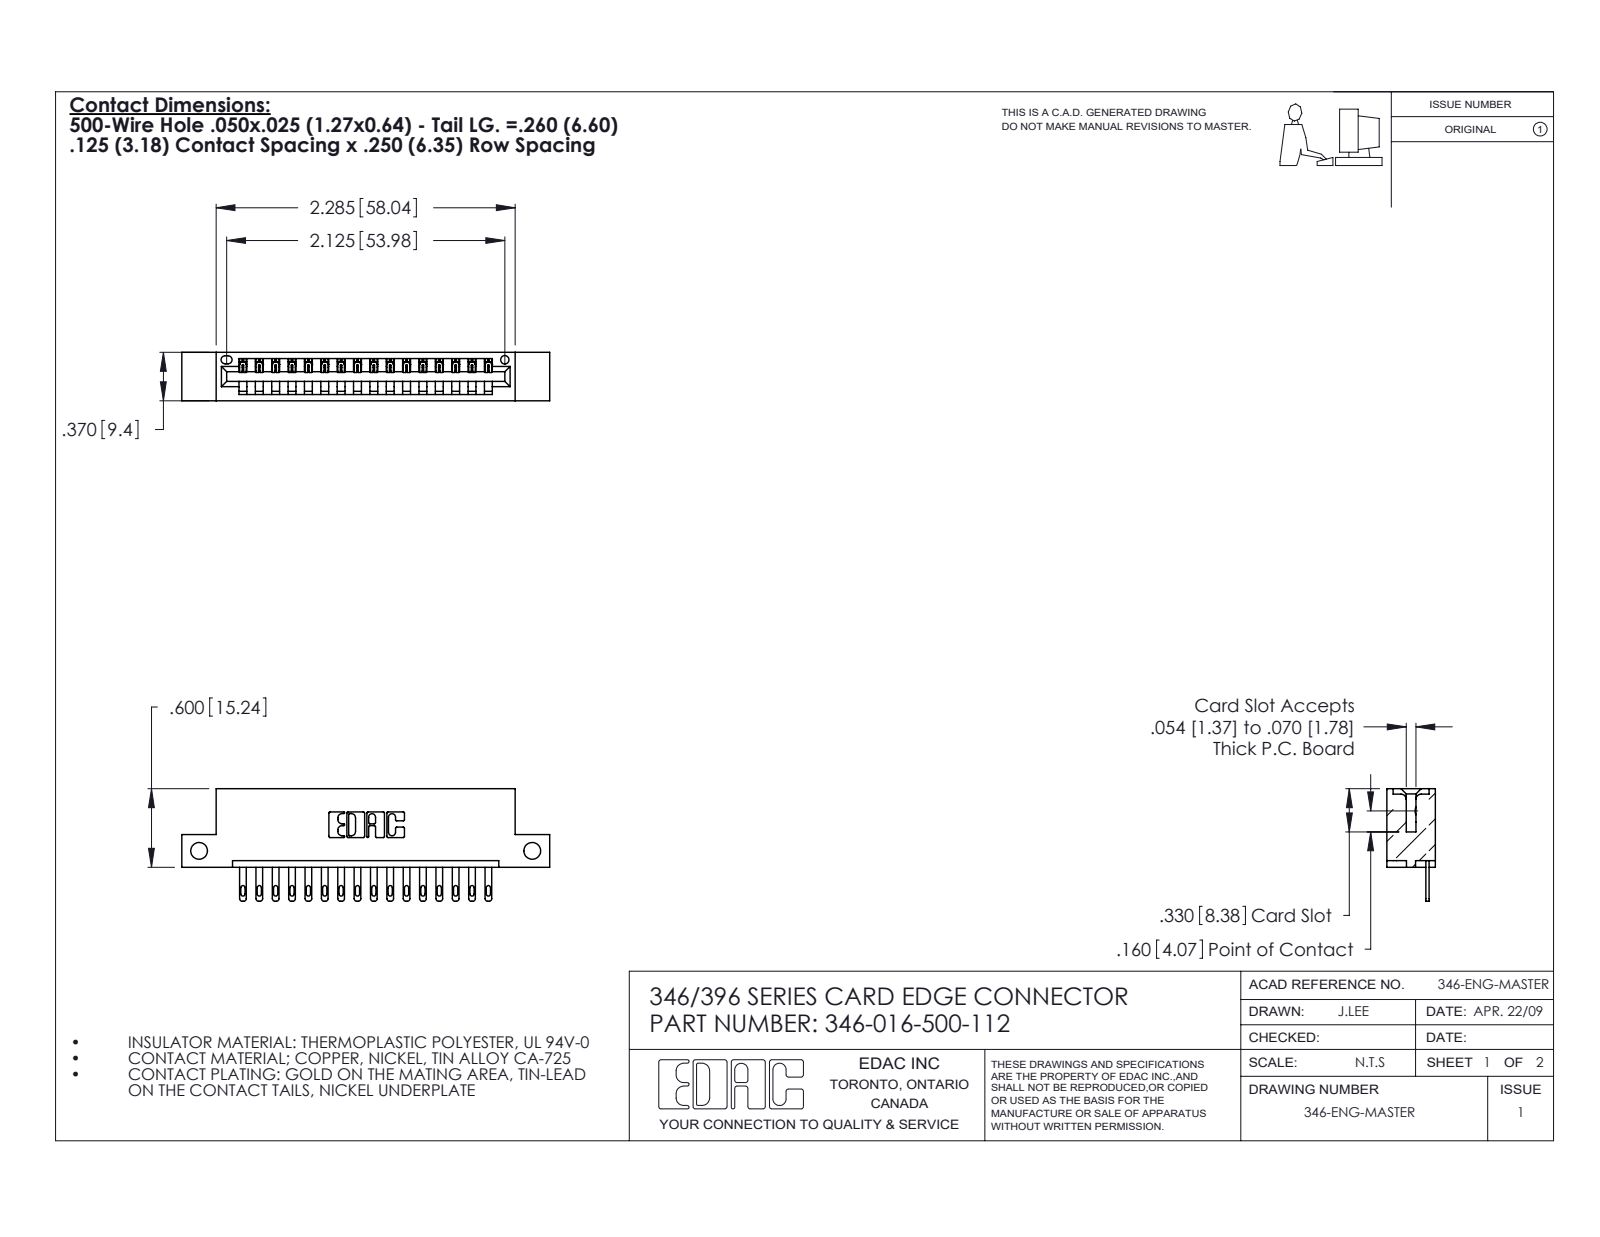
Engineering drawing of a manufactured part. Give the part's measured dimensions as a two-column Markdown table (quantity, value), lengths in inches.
| quantity | value |
| --- | --- |
| part name | 346-016-500-112; 346 Part_Flush Mounting Lugs - Side Mount; 345-292-001_345-293-100 |
| STEP written by | SolidWorks 2020 (CONFIG_CONTROL_DESIGN) |
| units | inches |
| bodies | 17 solids, 986 faces (620 planar, 366 cylindrical, 0 other) |
| overall size | 2.81 × 0.86 × 0.37 |
| volume | 0.401 in³ |
| surface area | 12.14 in² |
| round holes (diameter × count) | 0.128 × 2, 0.064 × 1 |
| partial cylindrical surfaces (radius × count) | 0.006 × 32, 0.016 × 32, 0.02 × 32, 0.01 × 22, 0.007 × 6, 0.031 × 6, 0.026 × 3, 0.031 × 2 |
| main face-to-face distances | 0.048, 0.322, 0.25, 0.37, 0.072, 0.298, 0.025, 0.148, 0.222, 0.1 |
| hole center spacings | 2.545 |
